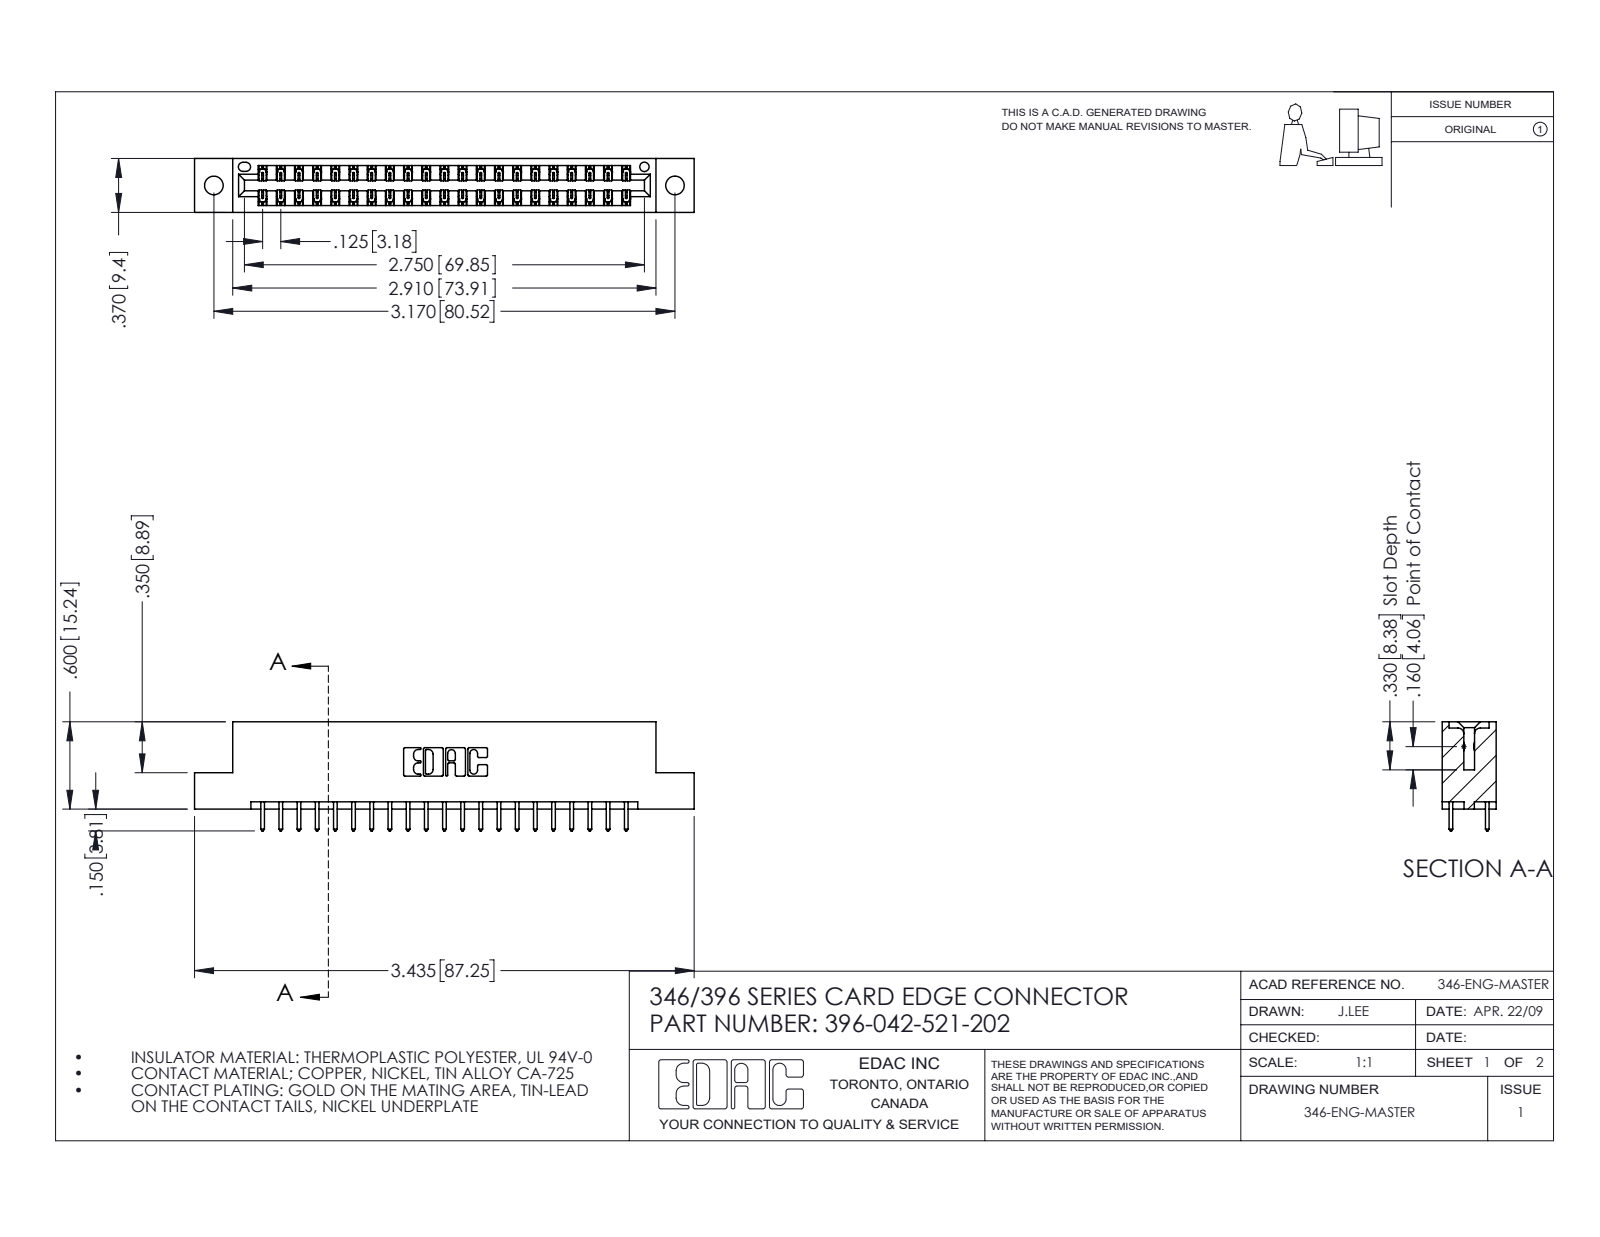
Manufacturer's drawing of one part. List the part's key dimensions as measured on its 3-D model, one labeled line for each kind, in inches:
Part name (STEP PRODUCT): 396-042-521-202; 345-292-001_345-293-121; 346 Part_Flush Mounting Lugs - 0.128 Dia
STEP written by: SolidWorks 2016 (CONFIG_CONTROL_DESIGN)
Units: inches
Bodies: 43 solids, 2306 faces (1546 planar, 760 cylindrical, 0 other)
Overall size (bounding box): 3.435 × 0.75 × 0.37
Volume: 0.506 in³ · Surface area: 16.56 in²
Round holes (diameter × count): ⌀0.128 ×2, ⌀0.064 ×1
Partial cylindrical surfaces — rounded edges, fillets, slot ends (radius × count): R0.006 ×63, R0.01 ×42, R0.01 ×22, R0.007 ×6, R0.031 ×6, R0.026 ×3, R0.014 ×2, R0.022 ×2
Main face-to-face distances: 0.048, 0.322, 0.25, 0.37, 0.072, 0.298, 0.025, 0.275, 0.148, 0.222
Hole centre spacings: 0.246, 2.963, 3.17
